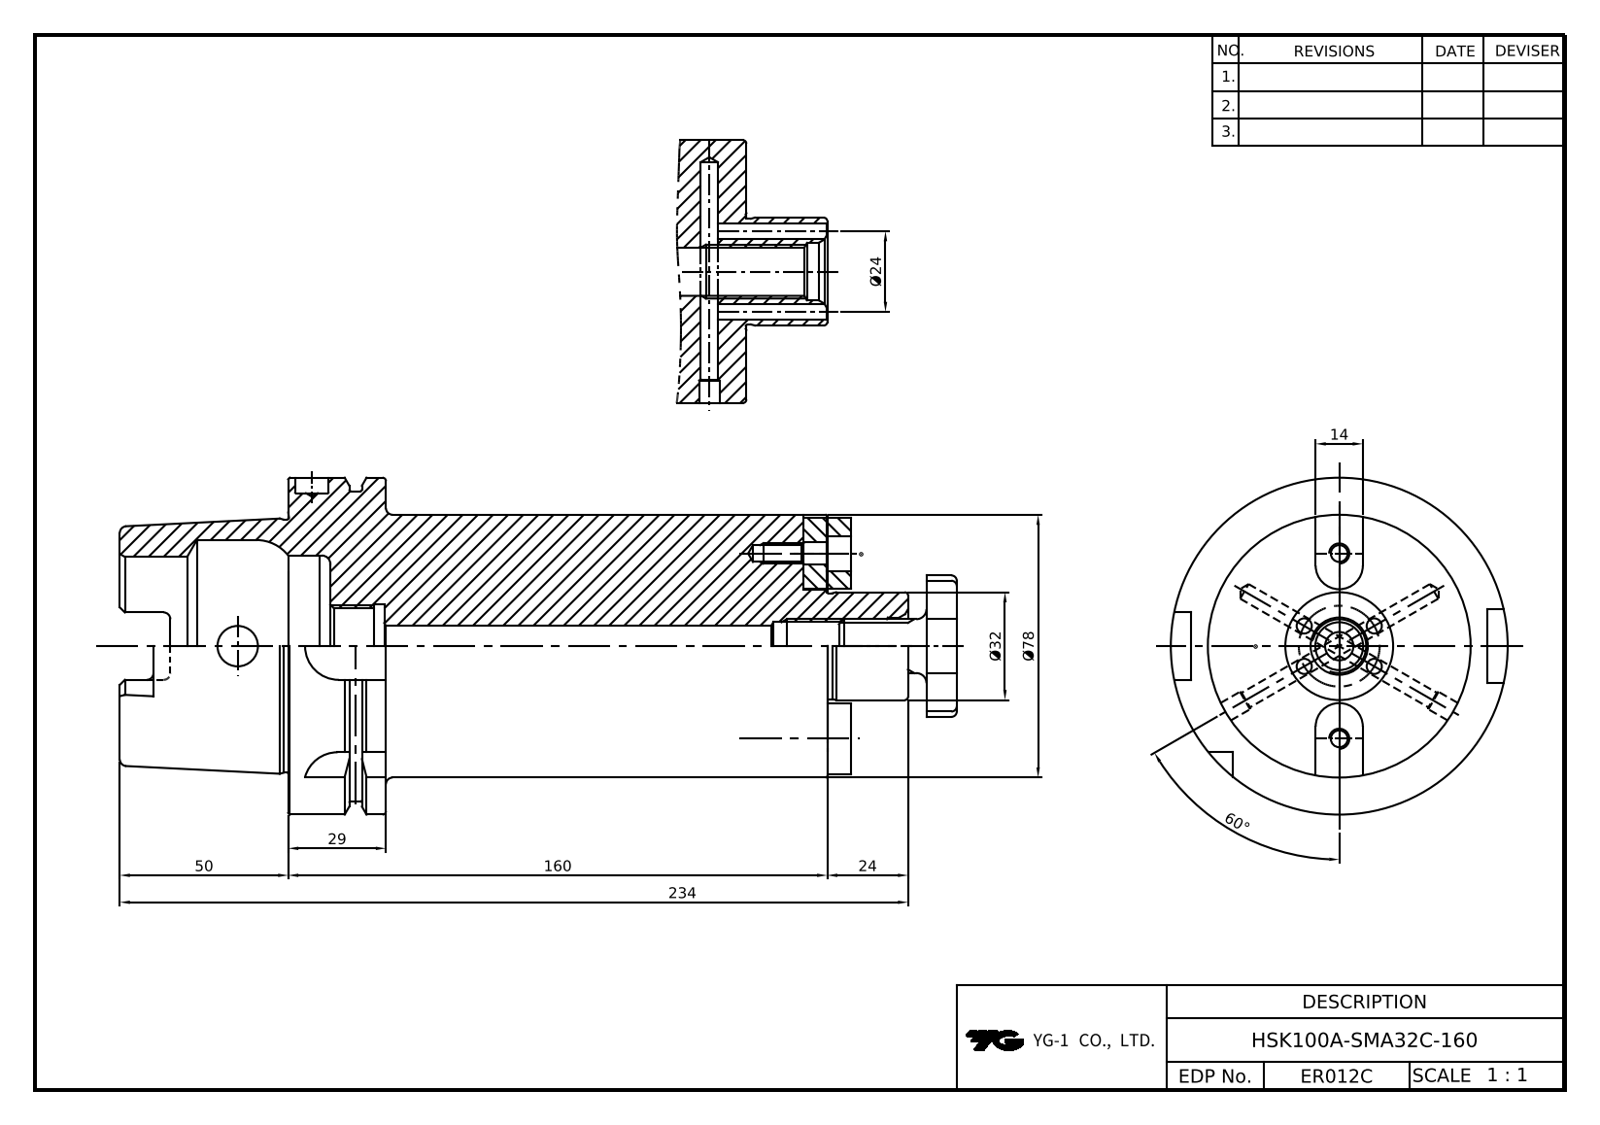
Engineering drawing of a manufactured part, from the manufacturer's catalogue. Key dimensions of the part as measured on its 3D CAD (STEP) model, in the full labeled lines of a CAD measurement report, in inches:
Part name (STEP PRODUCT): LO-HSK100A-SMA32C-160; SMA32E-DRIVE KEY-SECO; HEX'' WRENCH BOLT-M6x1.0x15L; SMA32-M16x2.0x26L
STEP written by: Autodesk Inventor 2025 (AP242_MANAGED_MODEL_BASED_3D_ENGINEERING_MIM_LF)
Units: inches
Bodies: 6 solids, 207 faces (85 planar, 62 cylindrical, 60 other)
Overall size (bounding box): 9.961 × 3.937 × 3.937
Volume: 54.86 in³ · Surface area: 158.2 in²
Round holes (diameter × count): ⌀0.177 ×4, ⌀0.194 ×2, ⌀0.26 ×2, ⌀0.394 ×2, ⌀0.413 ×2, ⌀0.472 ×1, ⌀0.545 ×1, ⌀0.669 ×1, ⌀0.881 ×1, ⌀0.984 ×1, ⌀2.087 ×1, ⌀2.48 ×1
Round bosses / shafts (diameter × count): ⌀0.394 ×2, ⌀0.236 ×2, ⌀3.937 ×1, ⌀3.622 ×1, ⌀3.071 ×1, ⌀2.969 ×1, ⌀1.26 ×1, ⌀0.63 ×1
Partial cylindrical surfaces — rounded edges, fillets, slot ends (radius × count): R0.079 ×6, R0.118 ×4, R0.192 ×4, R0.276 ×4, R0.394 ×4, R0.827 ×1
Main face-to-face distances: 6.299, 1.142, 5.157, 7.992, 1.969, 0.492, 0.65, 5.807, 0.276, 6.024
Hole centre spacings: 0.472, 0.94, 1.381, 0.818, 0.945, 1.083, 2.165
